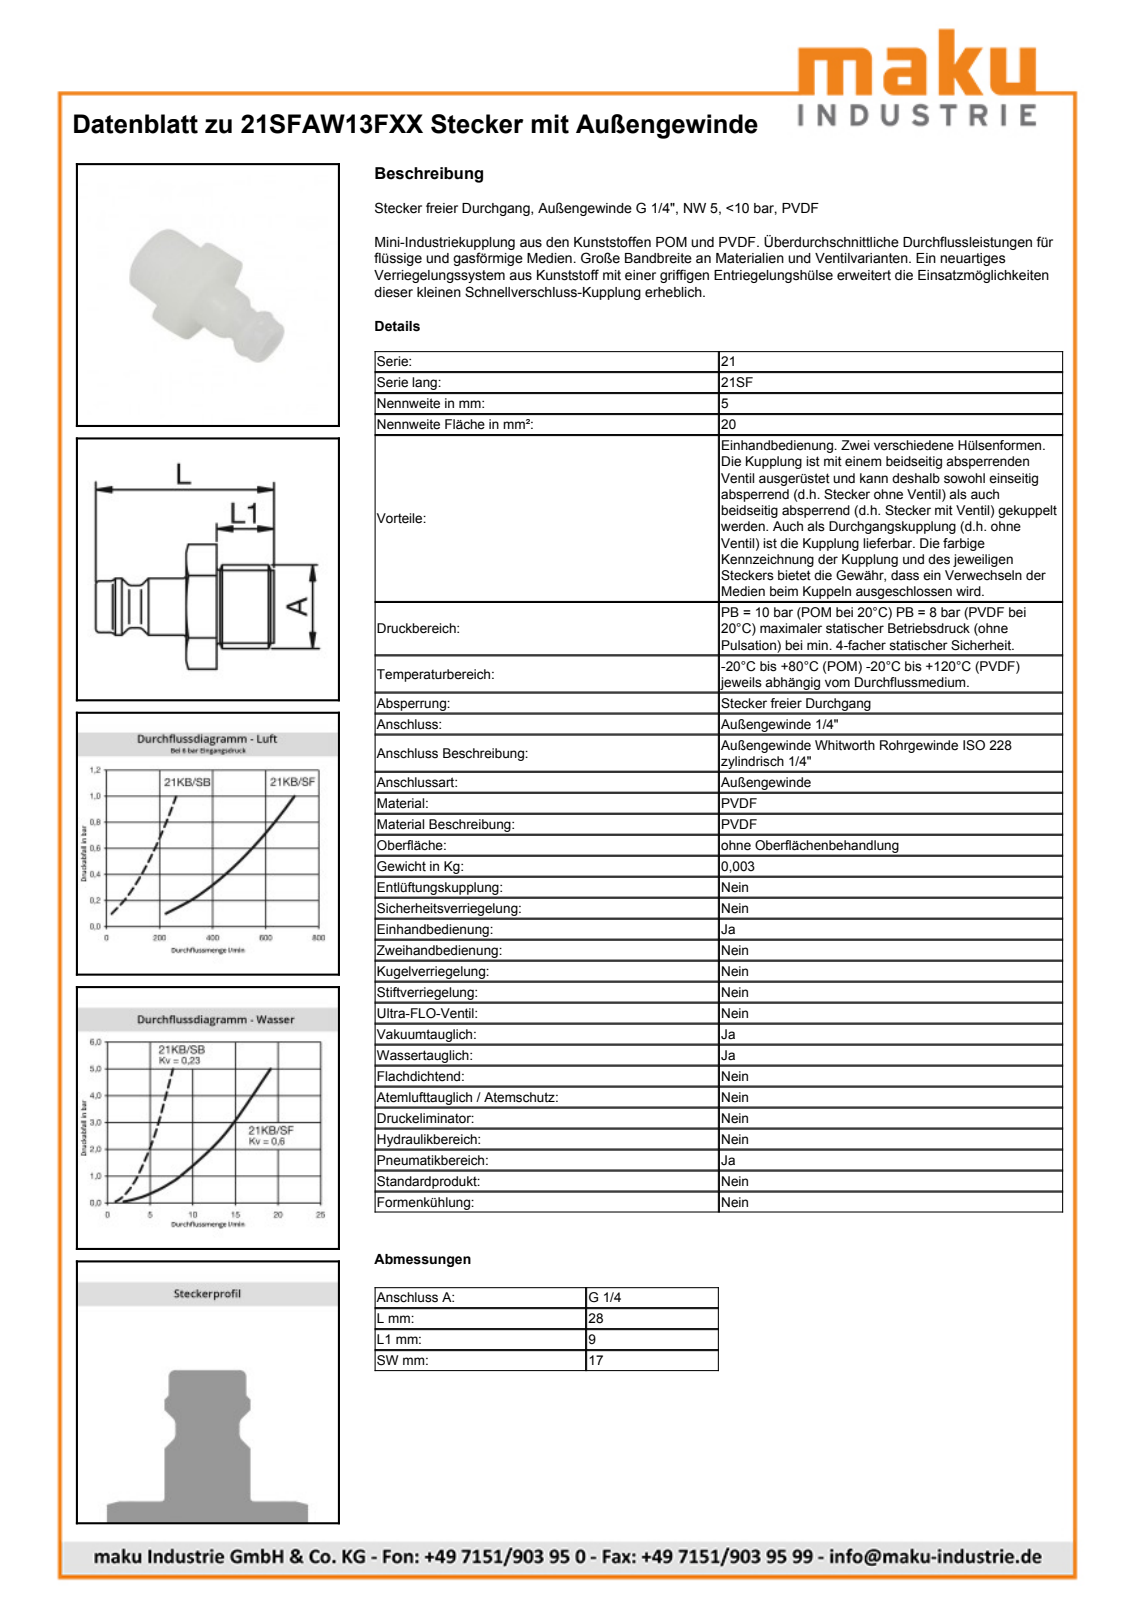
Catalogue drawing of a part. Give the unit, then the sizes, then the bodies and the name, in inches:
Units: inches
Overall size (bounding box): 1.083 × 0.754 × 0.669
Round holes (diameter × count): ⌀0.195 ×1
Round bosses / shafts (diameter × count): ⌀0.518 ×1, ⌀0.354 ×1, ⌀0.335 ×1, ⌀0.319 ×1, ⌀0.262 ×1
Partial cylindrical surfaces — rounded edges, fillets, slot ends (radius × count): R0.163 ×1, R0.377 ×1
Main face-to-face distances: 0.669, 0.173, 0.528, 0.354, 0.555, 0.728, 1.083, 0.485, 0.07, 0.243
Volume: 0.143 in³ · Surface area: 2.926 in²
Bodies: 1 solid, 291 faces (88 planar, 49 cylindrical, 154 other)
Part name (STEP PRODUCT): 21SFAW13FXX
STEP written by: Autodesk Inventor 2016 (AUTOMOTIVE_DESIGN)
